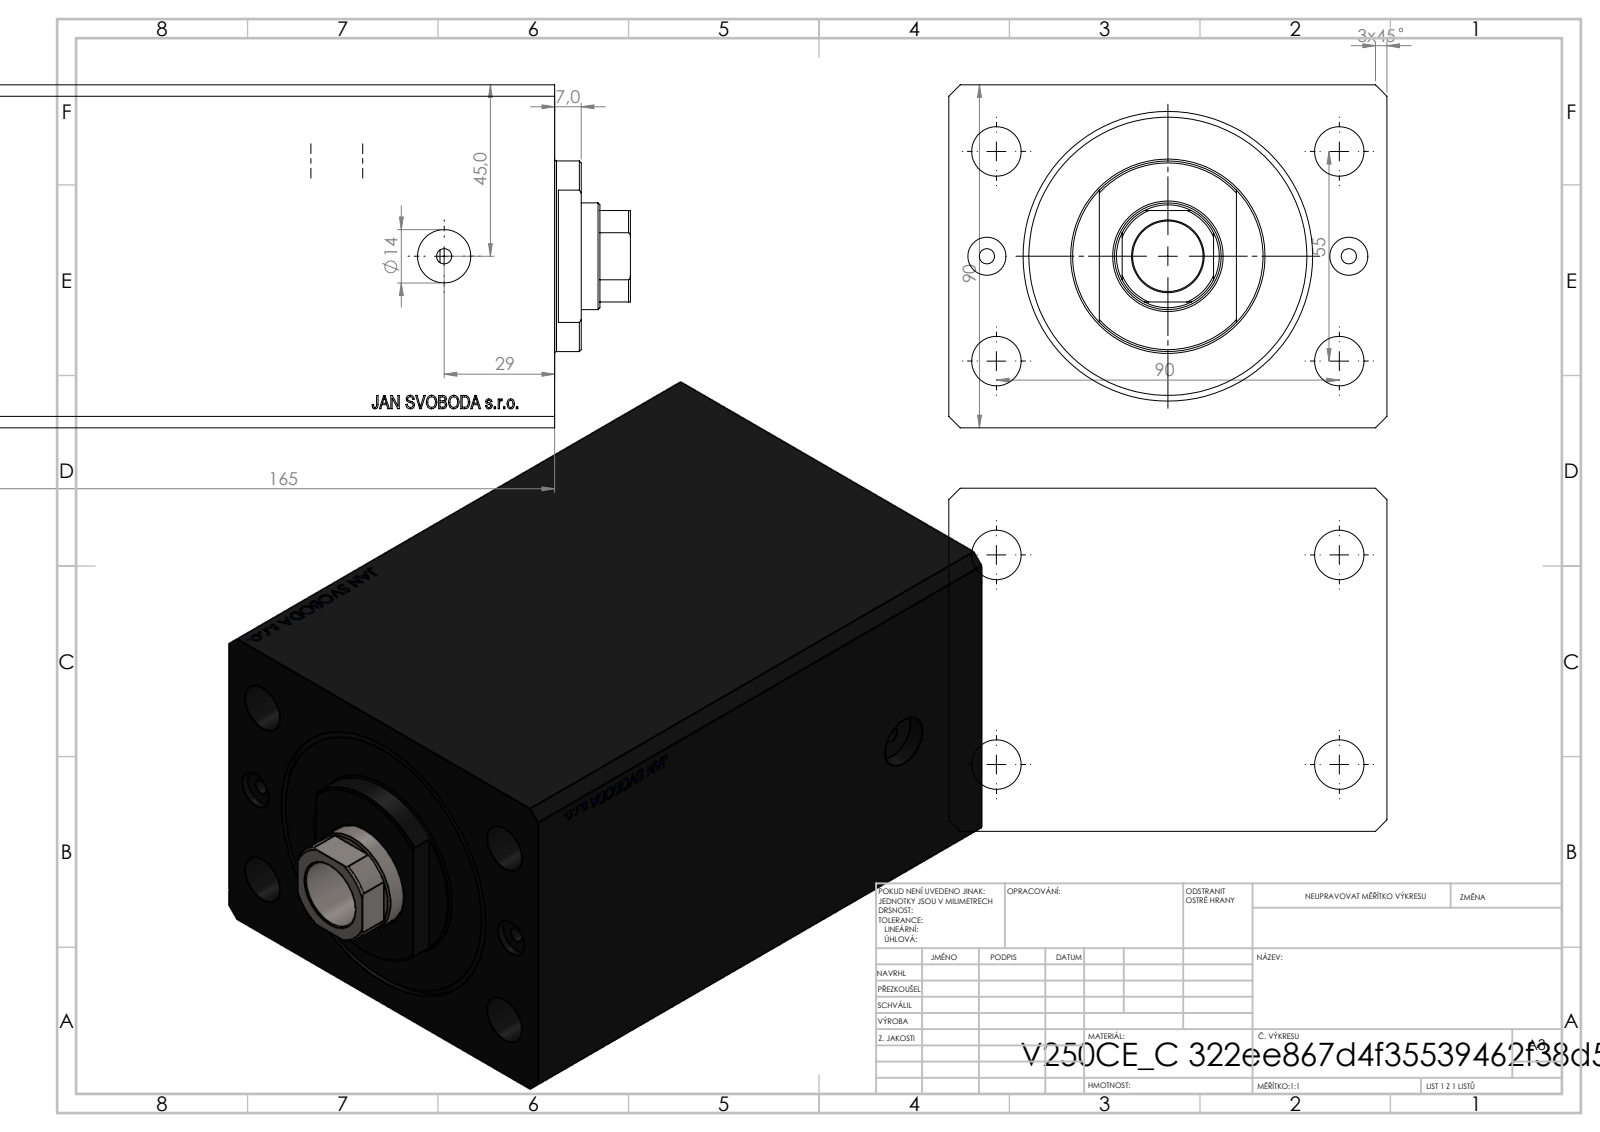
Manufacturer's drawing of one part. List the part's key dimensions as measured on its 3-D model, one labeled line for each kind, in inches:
Part name (STEP PRODUCT): V250CE_C_Body; V250CE_VC_C; V250CE_C_VCP
STEP written by: SolidWorks 2019 (CONFIG_CONTROL_DESIGN)
Units: inches
Bodies: 3 solids, 864 faces (428 planar, 44 cylindrical, 392 other)
Overall size (bounding box): 7.28 × 4.528 × 3.543
Volume: 86.84 in³ · Surface area: 297.1 in²
Round holes (diameter × count): ⌀0.157 ×4, ⌀0.512 ×4, ⌀0.394 ×2, ⌀0.551 ×2, ⌀0.728 ×1, ⌀1.102 ×1, ⌀2.48 ×1, ⌀2.992 ×1
Round bosses / shafts (diameter × count): ⌀1.969 ×1
Partial cylindrical surfaces — rounded edges, fillets, slot ends (radius × count): R0.531 ×1
Main face-to-face distances: 3.543, 4.528, 6.496, 0.705, 5.791, 5.311, 4.606, 1.185, 2.161, 3.15
Hole centre spacings: 1.087, 2.076, 3.799, 1.87, 2.165, 3.543, 4.153, 3.74
